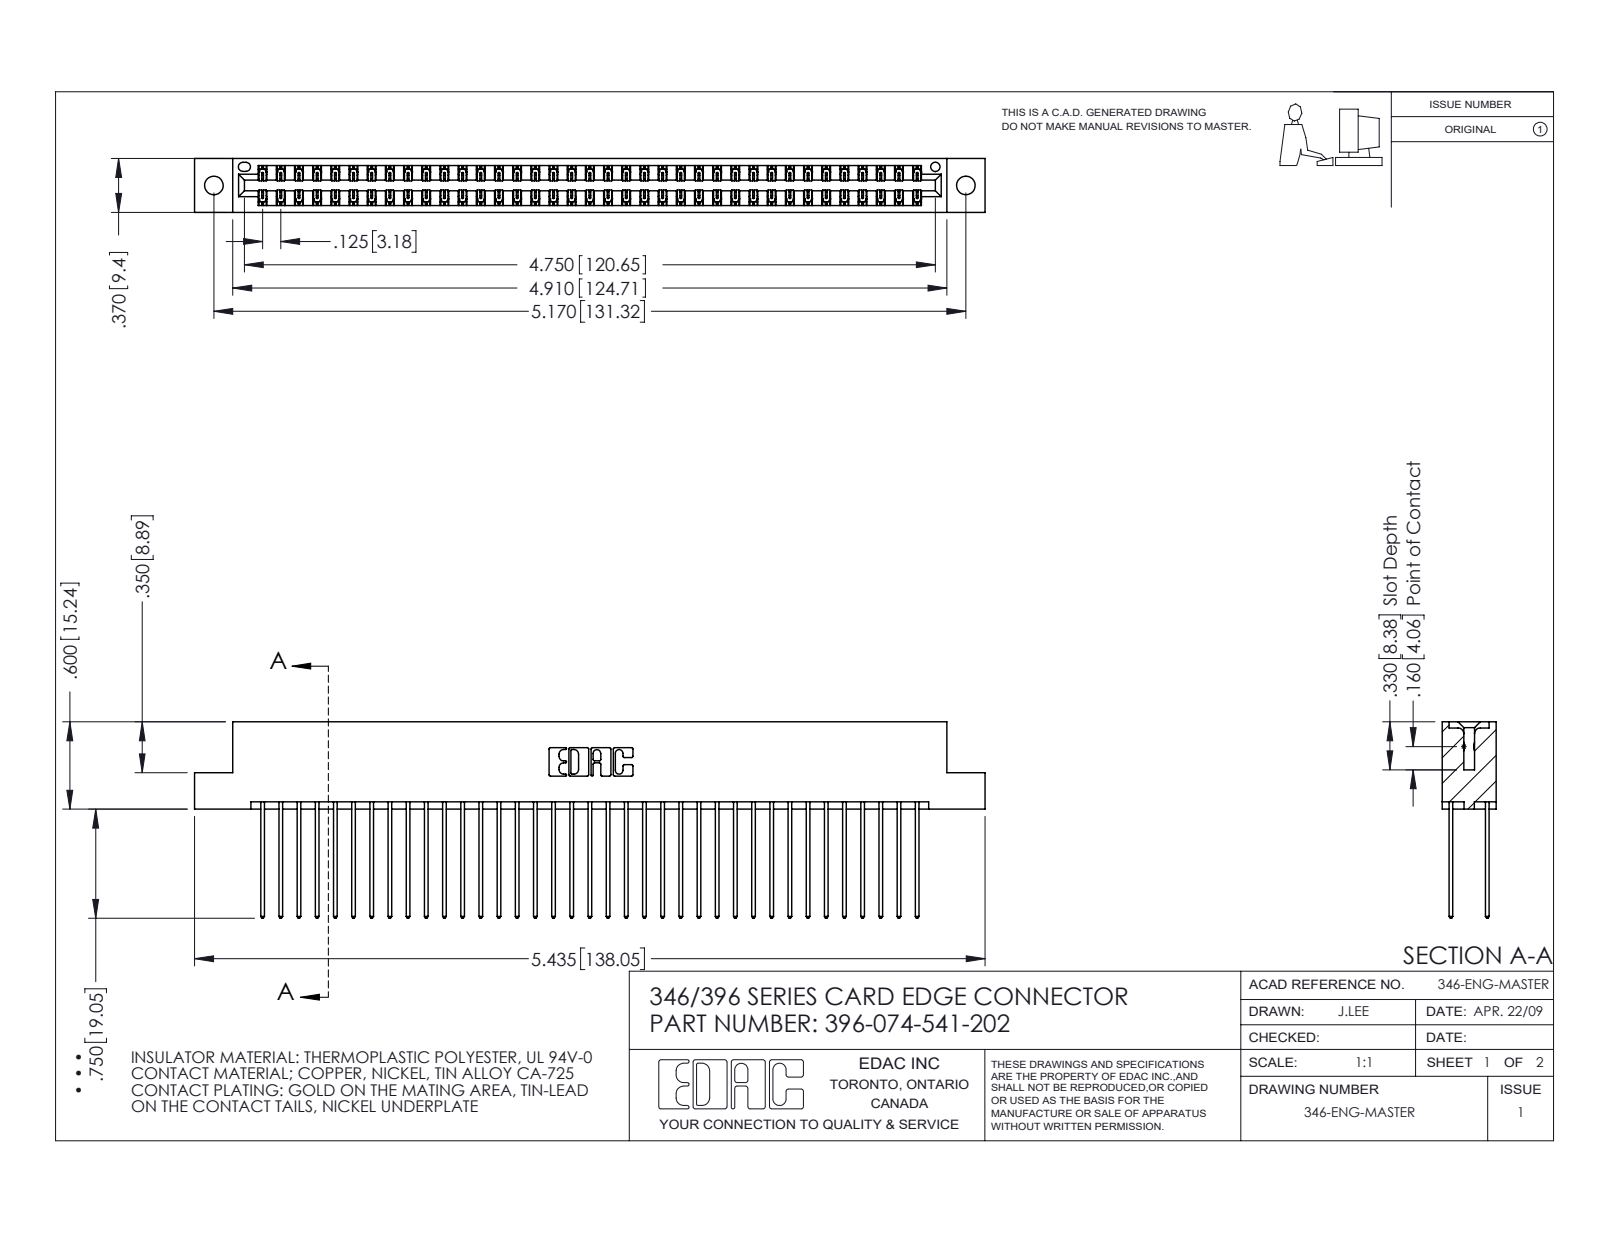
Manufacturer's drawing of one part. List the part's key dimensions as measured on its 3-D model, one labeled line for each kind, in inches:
Part name (STEP PRODUCT): 396-074-541-202; 345-292-001_345-293-141; 346 Part_Flush Mounting Lugs - 0.128 Dia
STEP written by: SolidWorks 2016 (CONFIG_CONTROL_DESIGN)
Units: inches
Bodies: 75 solids, 3970 faces (2666 planar, 1304 cylindrical, 0 other)
Overall size (bounding box): 5.435 × 1.35 × 0.37
Volume: 0.843 in³ · Surface area: 32.04 in²
Round holes (diameter × count): ⌀0.128 ×2, ⌀0.064 ×1
Partial cylindrical surfaces — rounded edges, fillets, slot ends (radius × count): R0.006 ×111, R0.01 ×74, R0.01 ×22, R0.007 ×6, R0.031 ×6, R0.026 ×3, R0.014 ×2, R0.022 ×2
Main face-to-face distances: 0.048, 0.322, 0.25, 0.072, 0.298, 0.025, 0.37, 0.275, 0.225, 0.148
Hole centre spacings: 0.246, 4.961, 5.17
